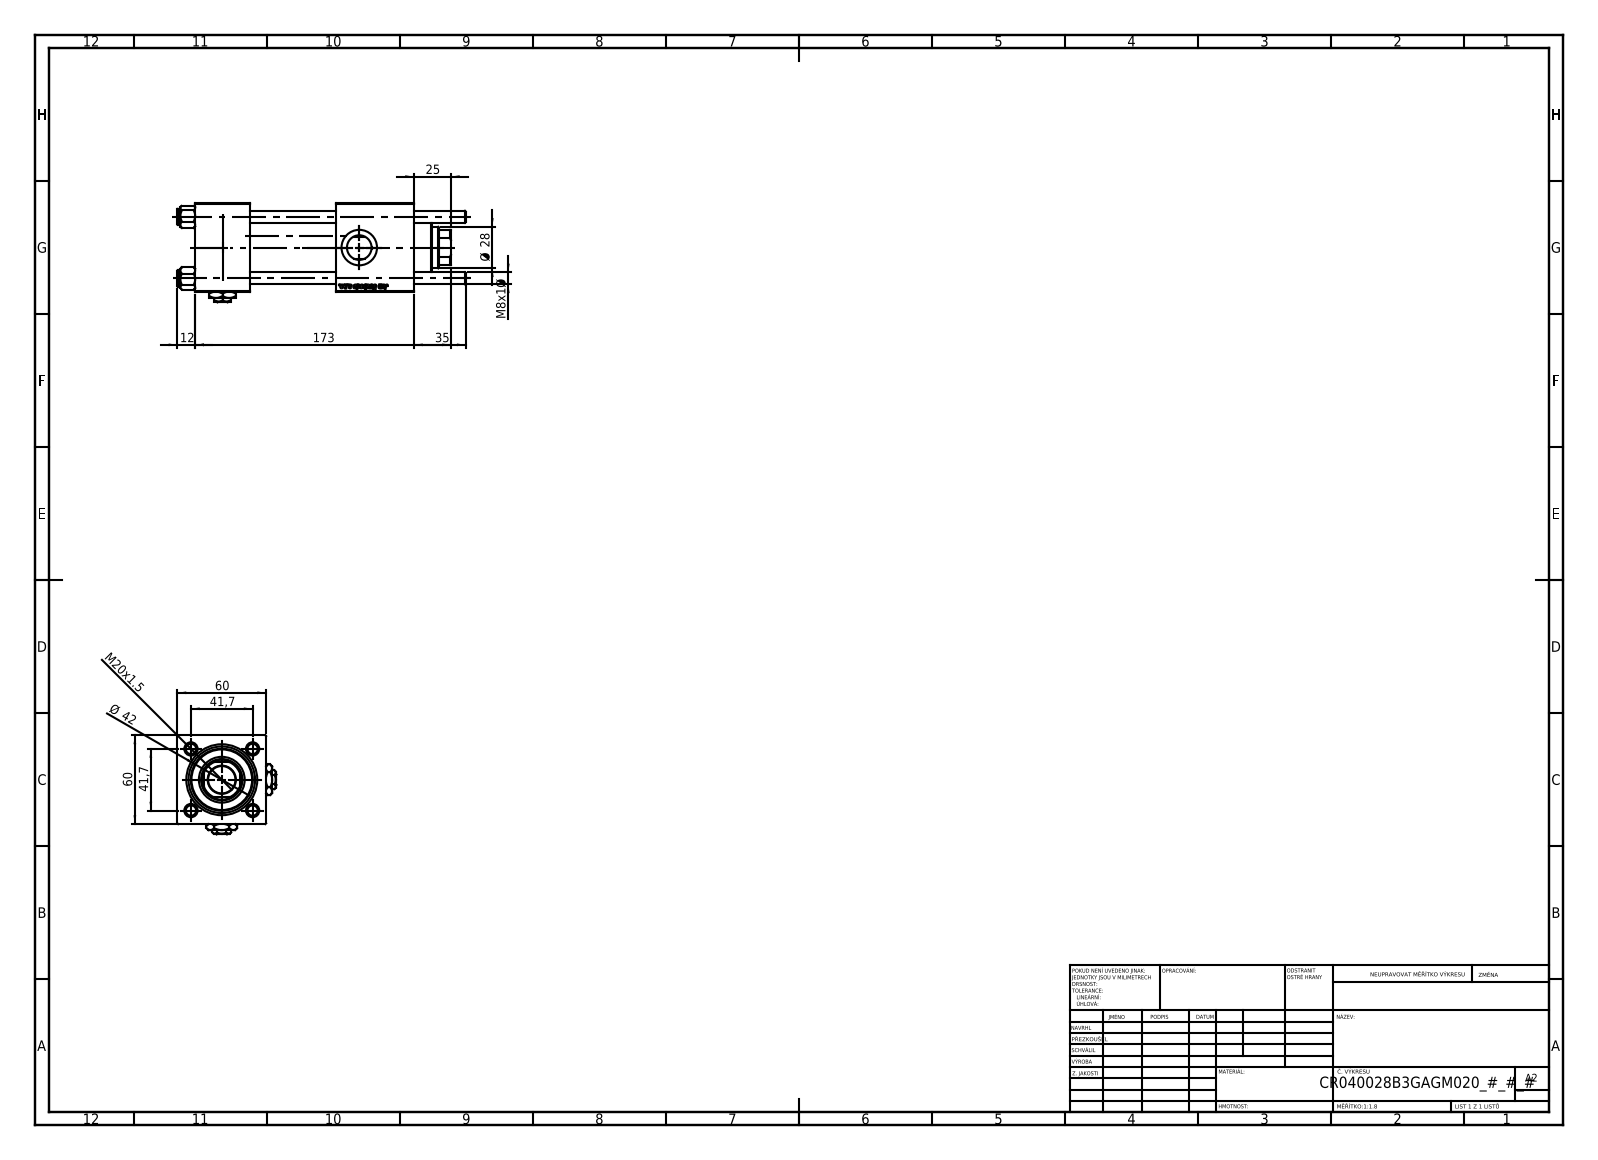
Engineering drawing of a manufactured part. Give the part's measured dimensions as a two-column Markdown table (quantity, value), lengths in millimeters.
| quantity | value |
| --- | --- |
| part name | V215CR_B_TYCINKA; V215CR_VCP_B; V215_VC_A; NUT_M5_B (+2 more) |
| STEP written by | SolidWorks 2019 (CONFIG_CONTROL_DESIGN) |
| units | millimeters |
| bodies | 13 solids, 1260 faces (480 planar, 90 cylindrical, 690 other) |
| overall size | 195 × 67 × 67 |
| volume | 431 626 mm³ |
| surface area | 122 974 mm² |
| round holes (diameter × count) | 8 × 4, 7 × 2, 16.66 × 2, 24 × 2, 16 × 1, 18.5 × 1, 28 × 1, 31 × 1, 40 × 1, 45 × 1 |
| round bosses / shafts (diameter × count) | 11 × 4, 46 × 1, 42 × 1 |
| partial cylindrical surfaces (radius × count) | 13.5 × 1 |
| main face-to-face distances | 60, 37, 58, 95, 53, 119.3, 82.3, 24.3, 148, 111 |
| hole center spacings | 29.49, 41.7, 58.97 |
